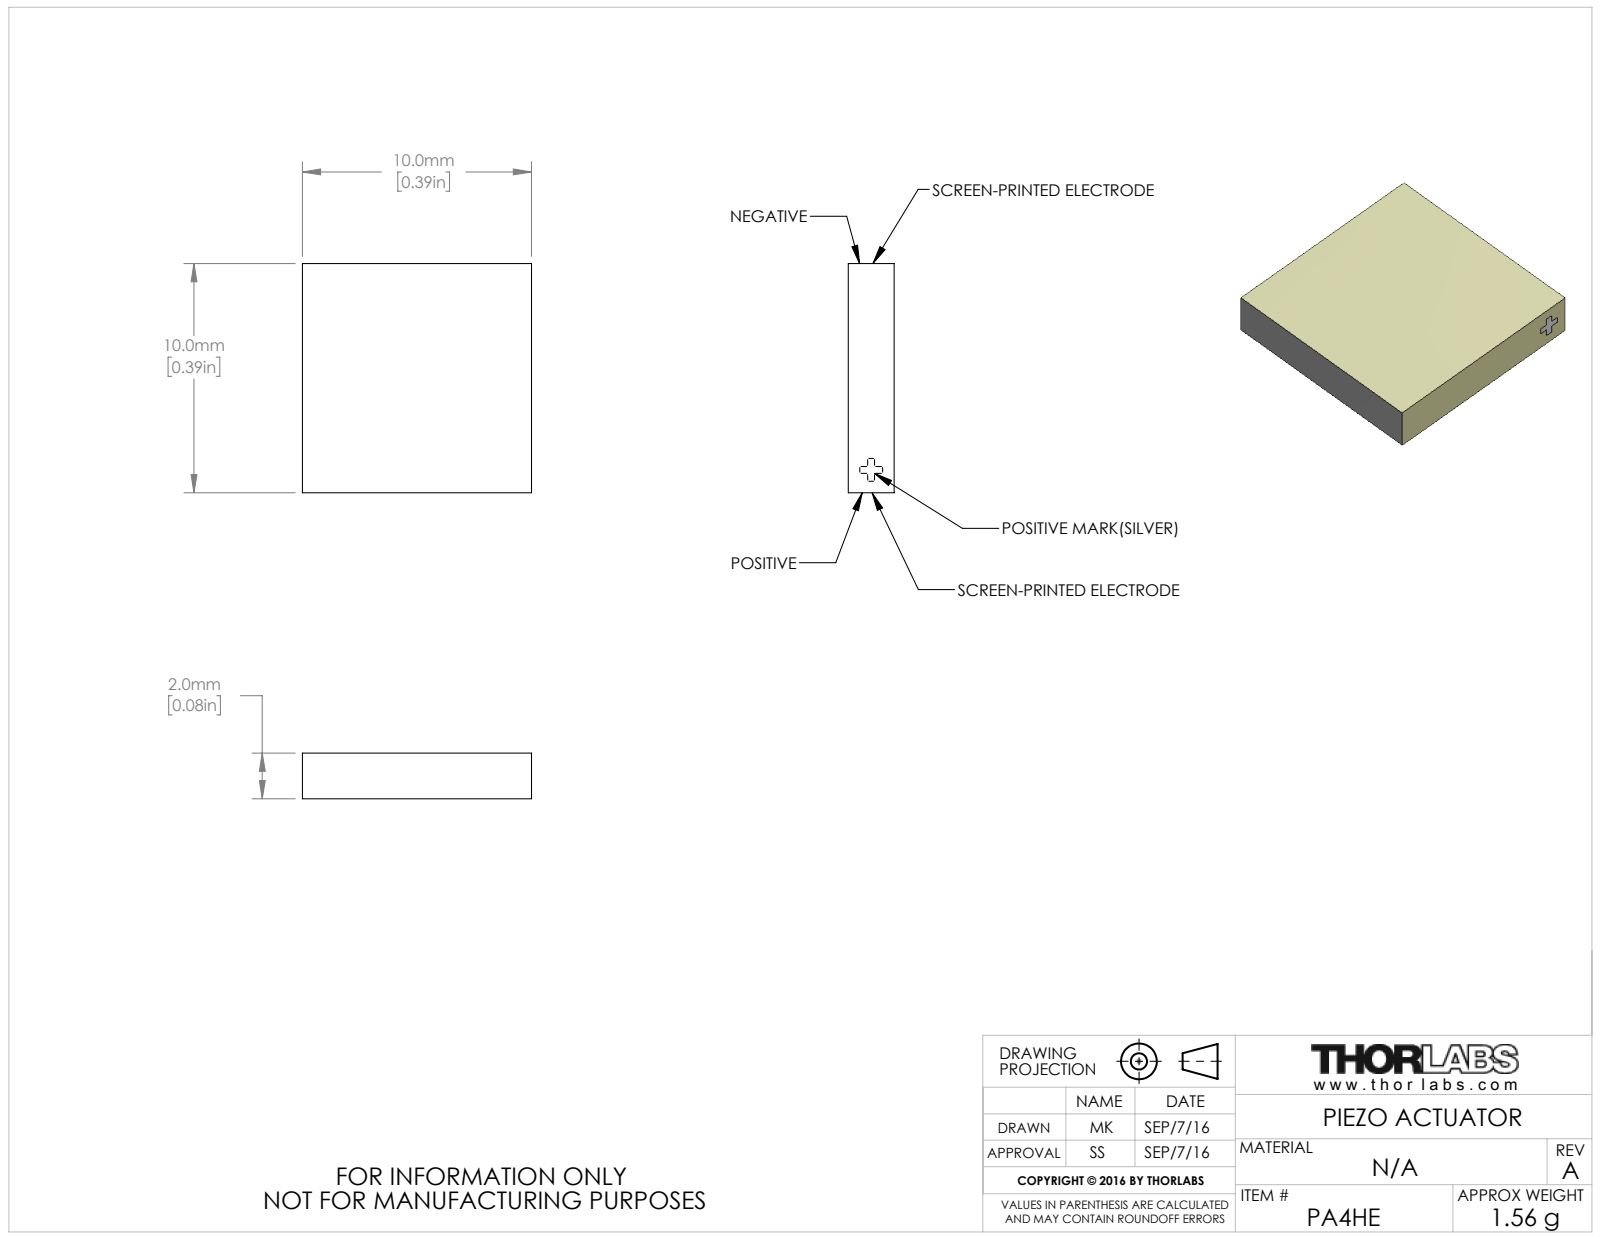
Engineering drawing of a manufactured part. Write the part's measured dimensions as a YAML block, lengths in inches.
part_name: "CTN002587"
step_written_by: "SolidWorks 2016 (AUTOMOTIVE_DESIGN)"
units: inches
bodies: {solids: 1, faces: 7, planar: 7, cylindrical: 0, other: 0}
overall_size: [0.394, 0.394, 0.079]
volume: 0.012
surface_area: 0.434
face_to_face_distances: [0.079, 0.394]
